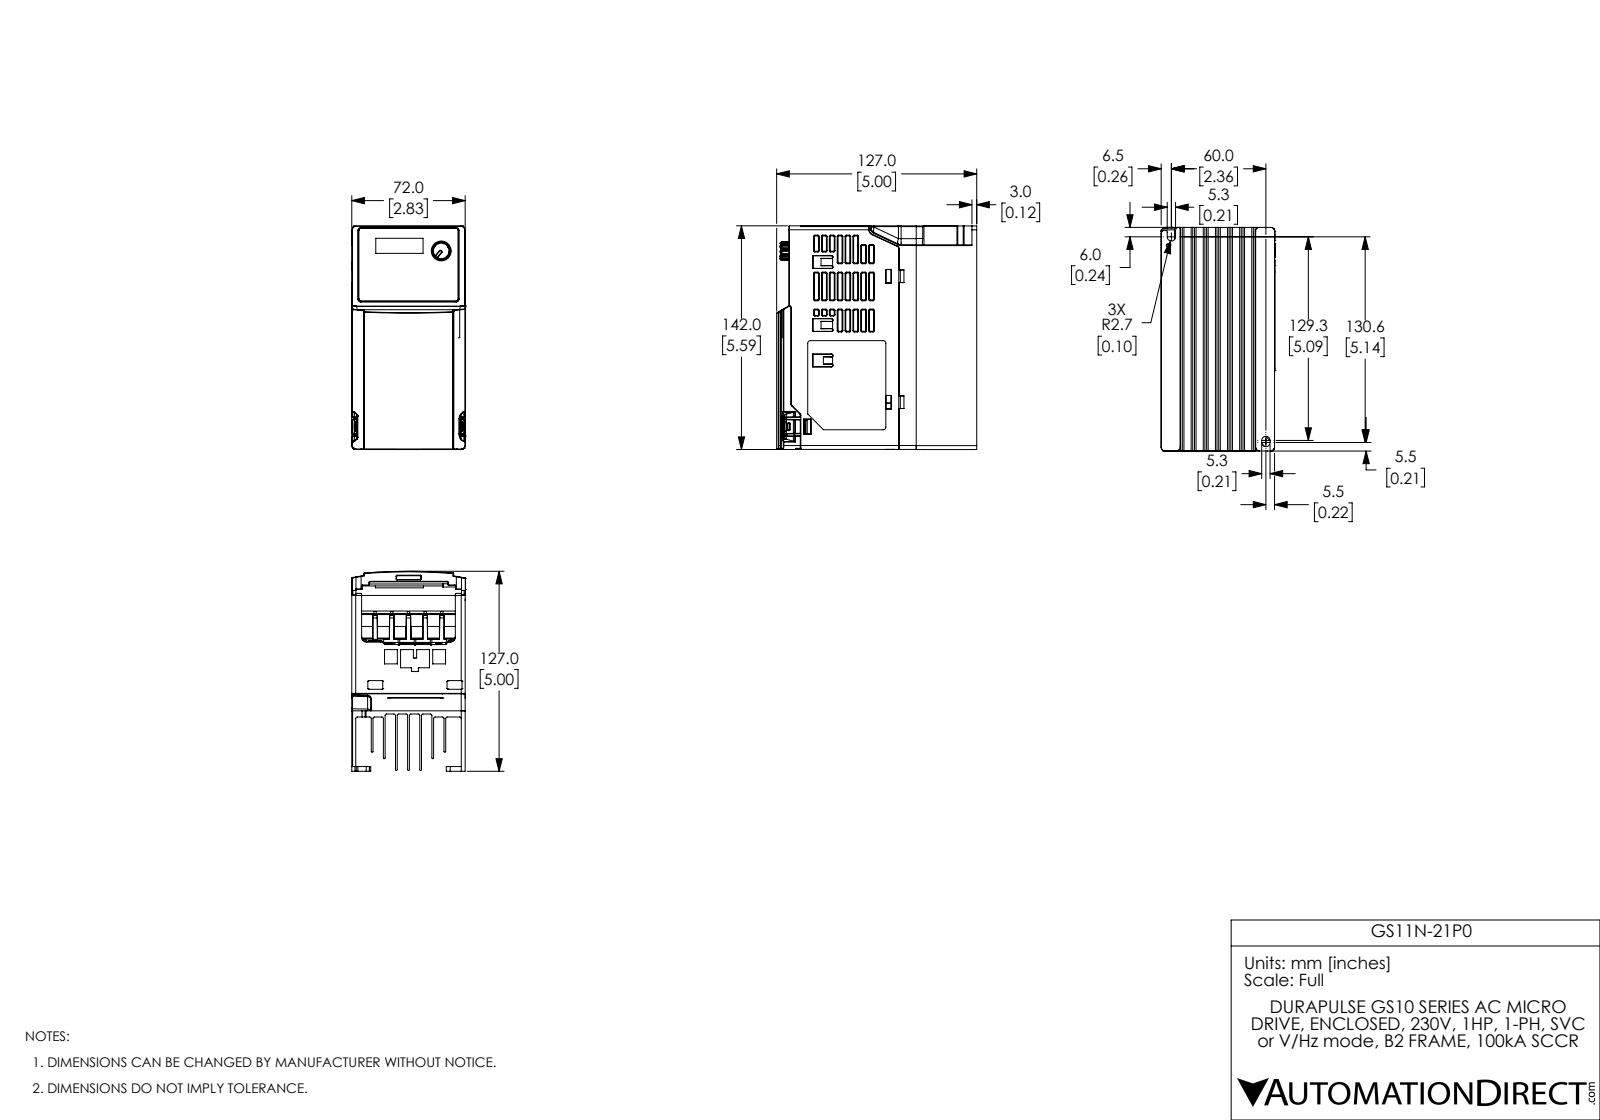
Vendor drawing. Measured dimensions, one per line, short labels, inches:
name: VFD-ME300-B3-PD-3D00-KEN_ASM REAR CASE n TermB ONLY 1 New 1B r3 COMPLETE 1knob cmb2b mod2 for B2C
written by: SolidWorks 2017 (AUTOMOTIVE_DESIGN)
unit: in
bodies: 9 solids, 4288 faces (2213 planar, 1220 cylindrical, 855 other)
size: 5.598 × 5 × 2.841
volume: 46.41 in³; area: 364.7 in²
holes: 4× ⌀0.169, 1× ⌀0.098, 1× ⌀0.429, 1× ⌀0.496
bosses: 4× ⌀0.268, 4× ⌀0.157
rounds: 315× R0.02, 128× R0.012, 55× R0.039, 45× R0.013, 14× R0.098, 13× R0.013, 13× R0.016, 11× R0.079
face distances: 0.303, 0.606, 0.043, 0.909, 0.26, 0.346, 0.563, 0.65, 0.039, 1.213
hole spacings: 0.402, 0.803, 0.8, 1.202, 1.205, 1.604, 2.005, 4.534
